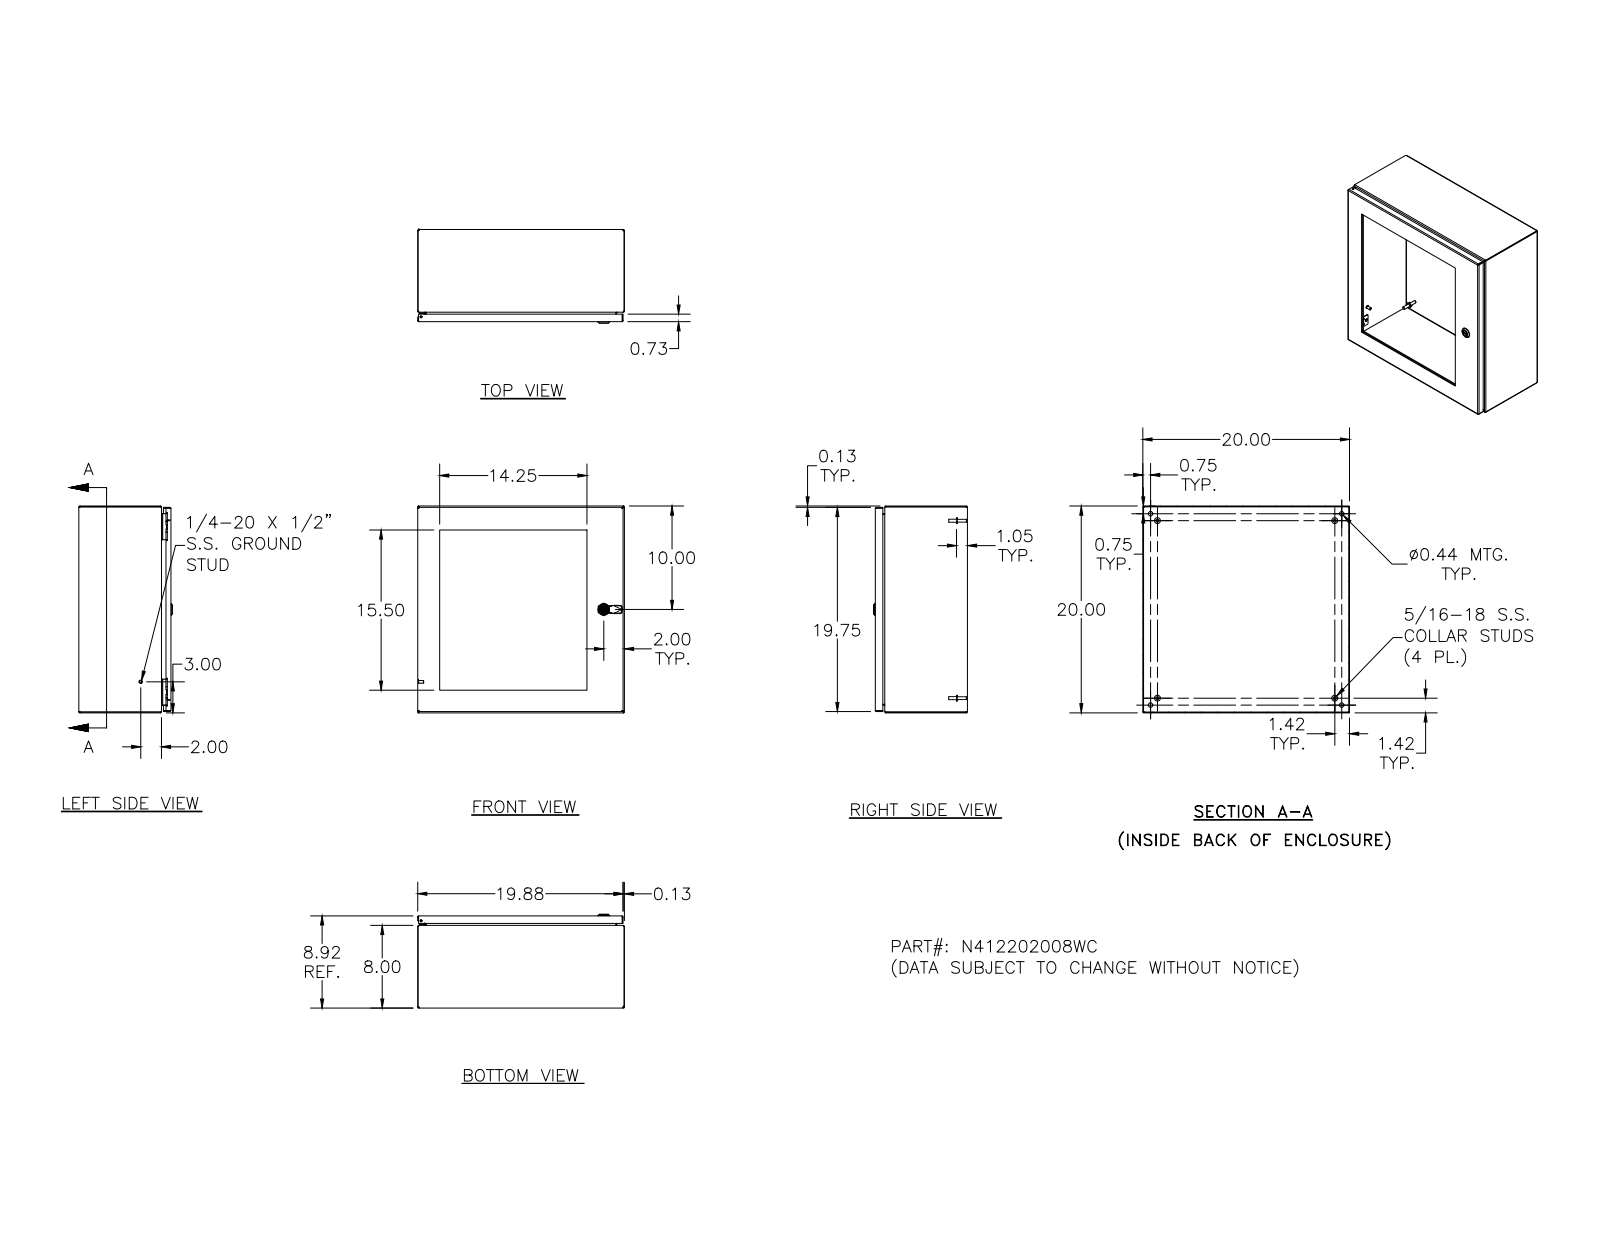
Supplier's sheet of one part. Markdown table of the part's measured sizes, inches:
| quantity | value |
| --- | --- |
| part name | N412202008WC |
| STEP written by | SolidWorks 2018 (AUTOMOTIVE_DESIGN) |
| units | inches |
| bodies | 69 solids, 2019 faces (753 planar, 617 cylindrical, 649 other) |
| overall size | 20 × 20 × 9.075 |
| volume | 170.6 in³ |
| surface area | 3 465 in² |
| round holes (diameter × count) | 0.156 × 18, 0.281 × 16, 0.188 × 5, 0.093 × 4, 0.152 × 4, 0.167 × 4, 0.172 × 4, 0.437 × 4, 0.187 × 1, 0.197 × 1, 0.315 × 1, 0.394 × 1 |
| round bosses / shafts (diameter × count) | 0.337 × 16, 0.19 × 16, 0.25 × 10, 0.563 × 4, 0.36 × 4, 0.32 × 4, 0.3 × 4, 0.275 × 4 |
| partial cylindrical surfaces (radius × count) | 0.031 × 34, 0.012 × 30, 0.05 × 26, 0.105 × 24, 0.016 × 18, 0.125 × 16, 0.02 × 13, 0.032 × 8 |
| main face-to-face distances | 0.074, 19.926, 8.843, 8.769, 20, 19.852, 0.25, 8.593, 8.519, 8.917 |
| hole center spacings | 4, 8, 16.008, 16, 17.221, 6.221, 8.585, 10.035 |
